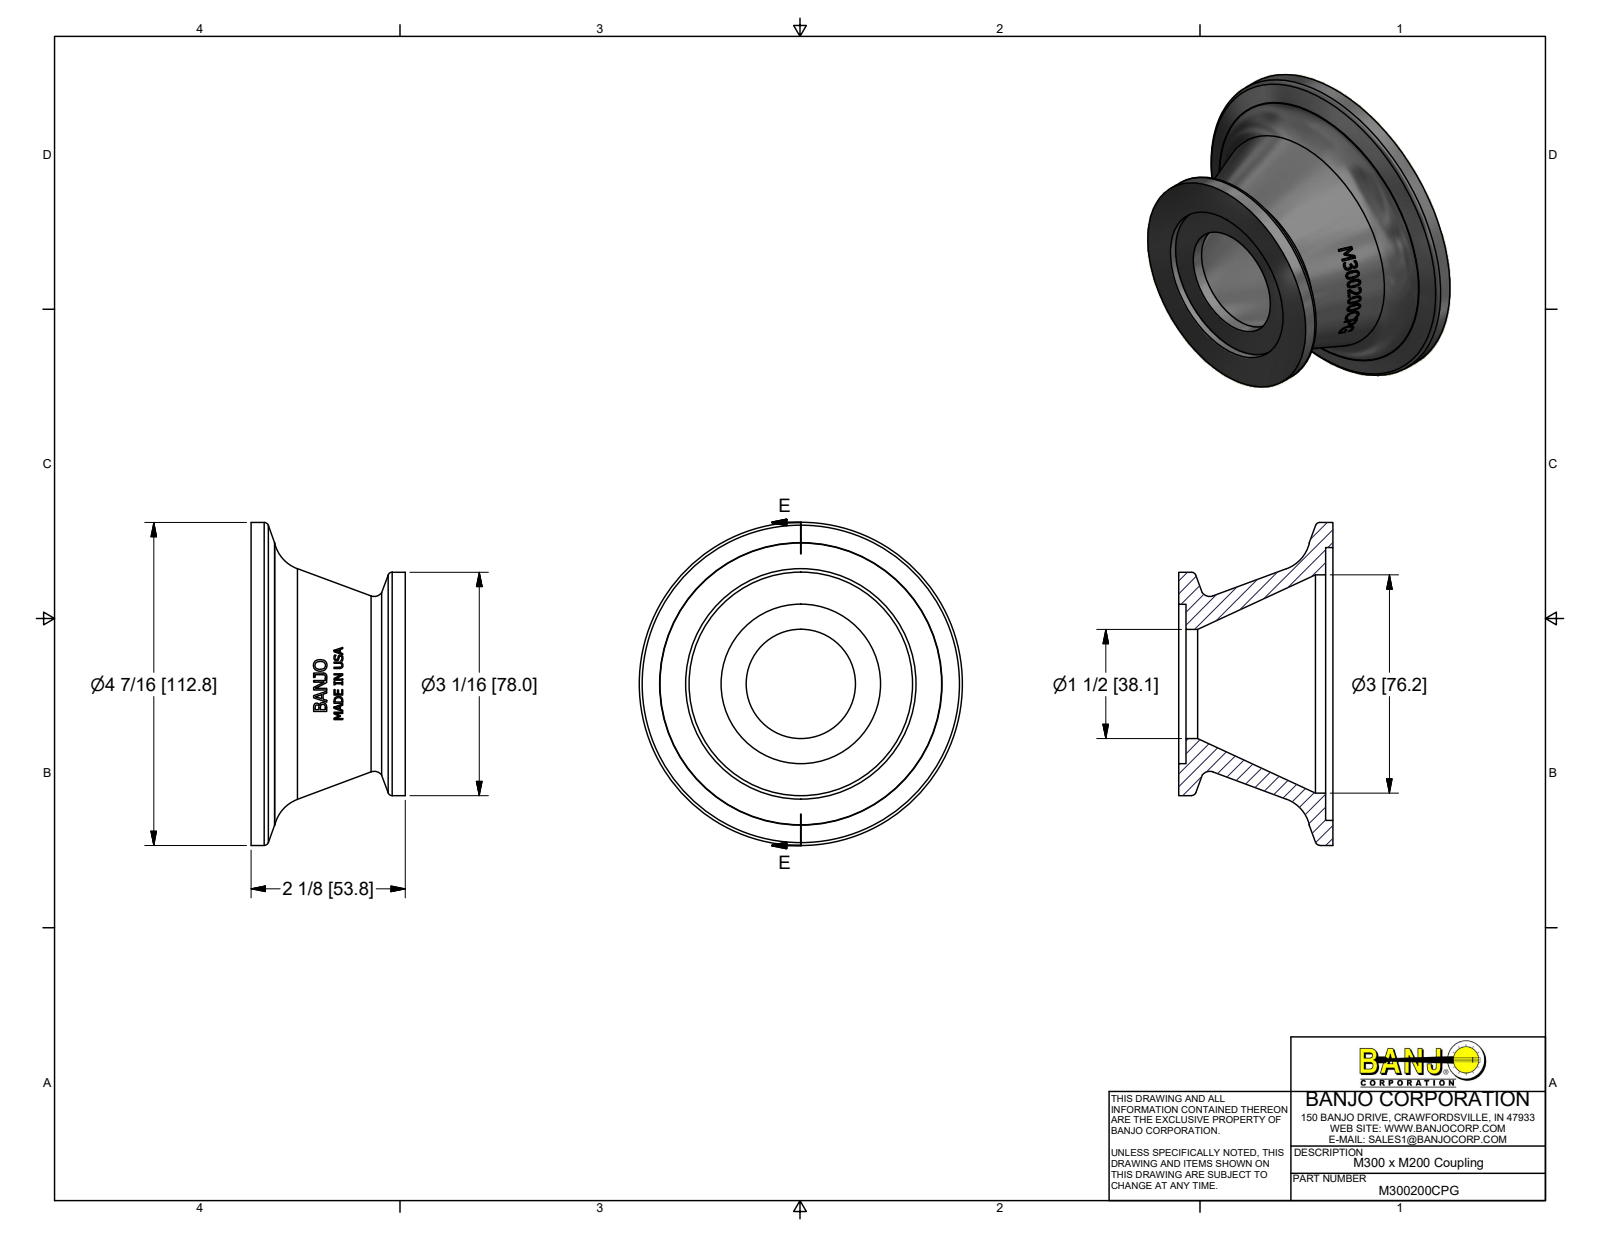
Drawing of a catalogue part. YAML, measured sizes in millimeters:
part_name: "M300200CPG"
step_written_by: "Autodesk Inventor 2016 (AUTOMOTIVE_DESIGN)"
units: millimeters
bodies: {solids: 1, faces: 405, planar: 173, cylindrical: 6, other: 226}
overall_size: [112.78, 112.78, 53.85]
volume: 121606
surface_area: 37967
round_holes:
  - {diameter: 38.1, count: 1}
  - {diameter: 55.63, count: 1}
  - {diameter: 76.2, count: 1}
  - {diameter: 95.25, count: 1}
round_bosses_or_shafts:
  - {diameter: 112.78, count: 1}
  - {diameter: 77.98, count: 1}
face_to_face_distances: [2.54, 51.3, 53.84, 48.76, 10.18, 16.79, 0.56, 21.85, 0.61, 25.89]
